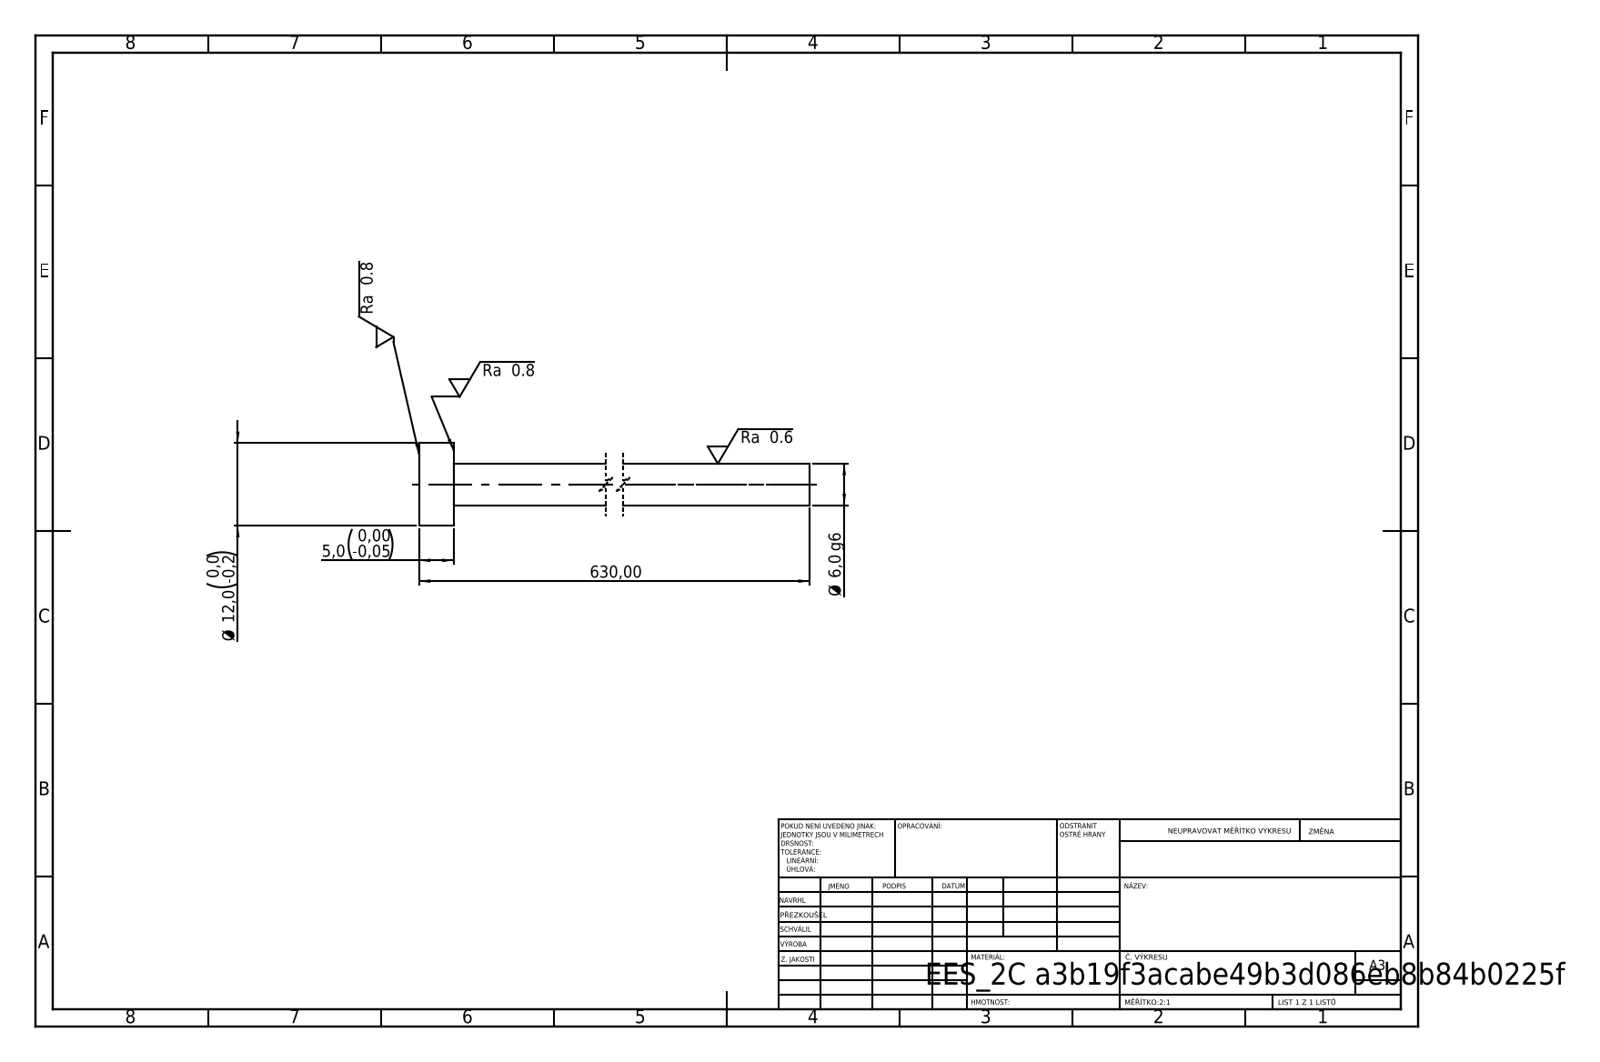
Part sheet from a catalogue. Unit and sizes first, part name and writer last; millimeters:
Units: millimetres
Overall size (bounding box): 630 × 12 × 12
Round bosses / shafts (diameter × count): ⌀12 ×1, ⌀6 ×1
Main face-to-face distances: 5, 630, 625
Volume: 18 237 mm³ · Surface area: 12 196 mm²
Bodies: 1 solid, 7 faces (3 planar, 4 cylindrical, 0 other)
STEP written by: SolidWorks 2019 (CONFIG_CONTROL_DESIGN)
